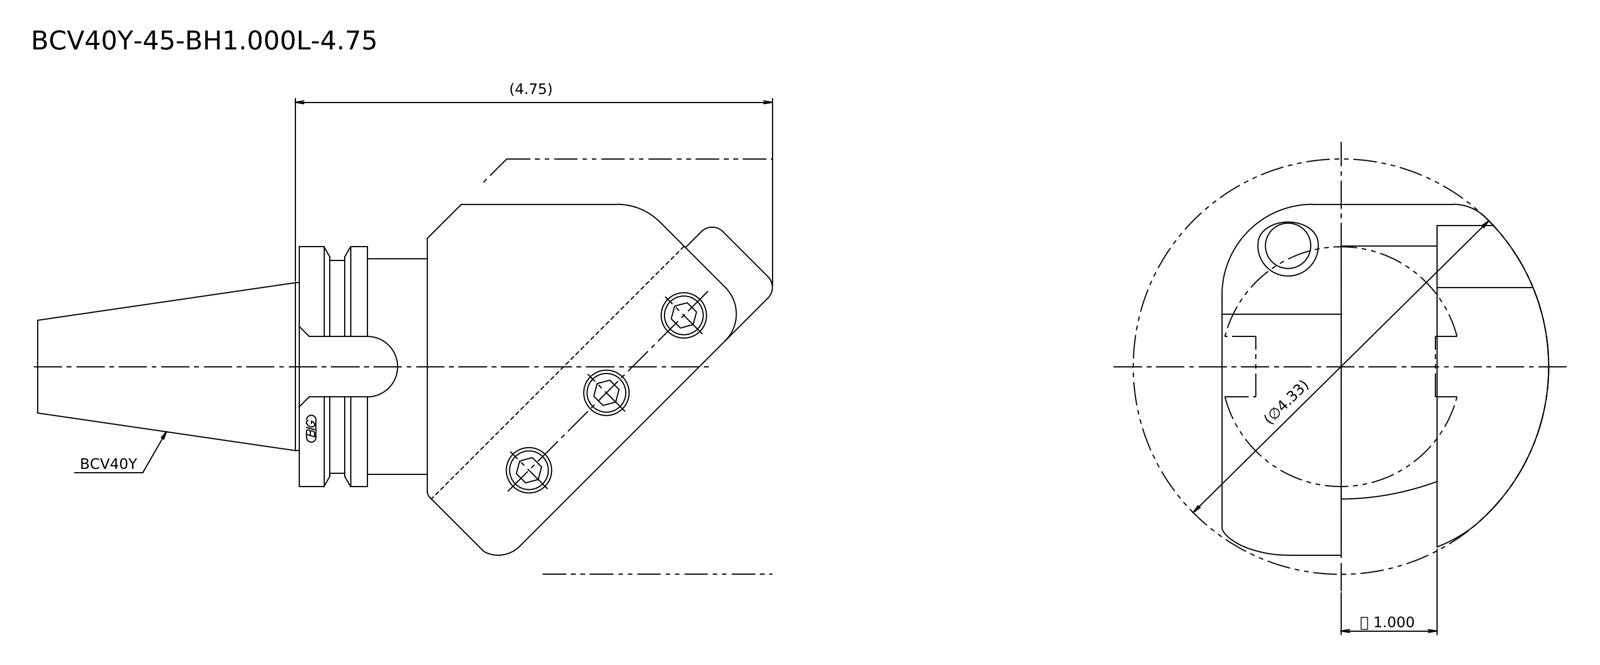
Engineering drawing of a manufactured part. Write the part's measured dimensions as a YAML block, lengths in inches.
step_written_by: "Kubotek KeyCreator 2011 V10.0.2 (22737) (automotive_design)"
units: inches
bodies: {solids: 1, faces: 29, planar: 16, cylindrical: 9, other: 4}
overall_size: [7.726, 3.78, 3.415]
volume: 31.06
surface_area: 77.18
round_bosses_or_shafts:
  - {diameter: 2.5, count: 1}
  - {diameter: 2.244, count: 1}
  - {diameter: 2.219, count: 1}
  - {diameter: 1.75, count: 1}
partial_cylinders:
  - {radius: 0.472, count: 1}
  - {radius: 0.945, count: 1}
  - {radius: 2.165, count: 1}
face_to_face_distances: [1, 2.24, 1.24, 1.339, 0.628, 0.711, 0.394, 4.065, 3.437, 2.726]
